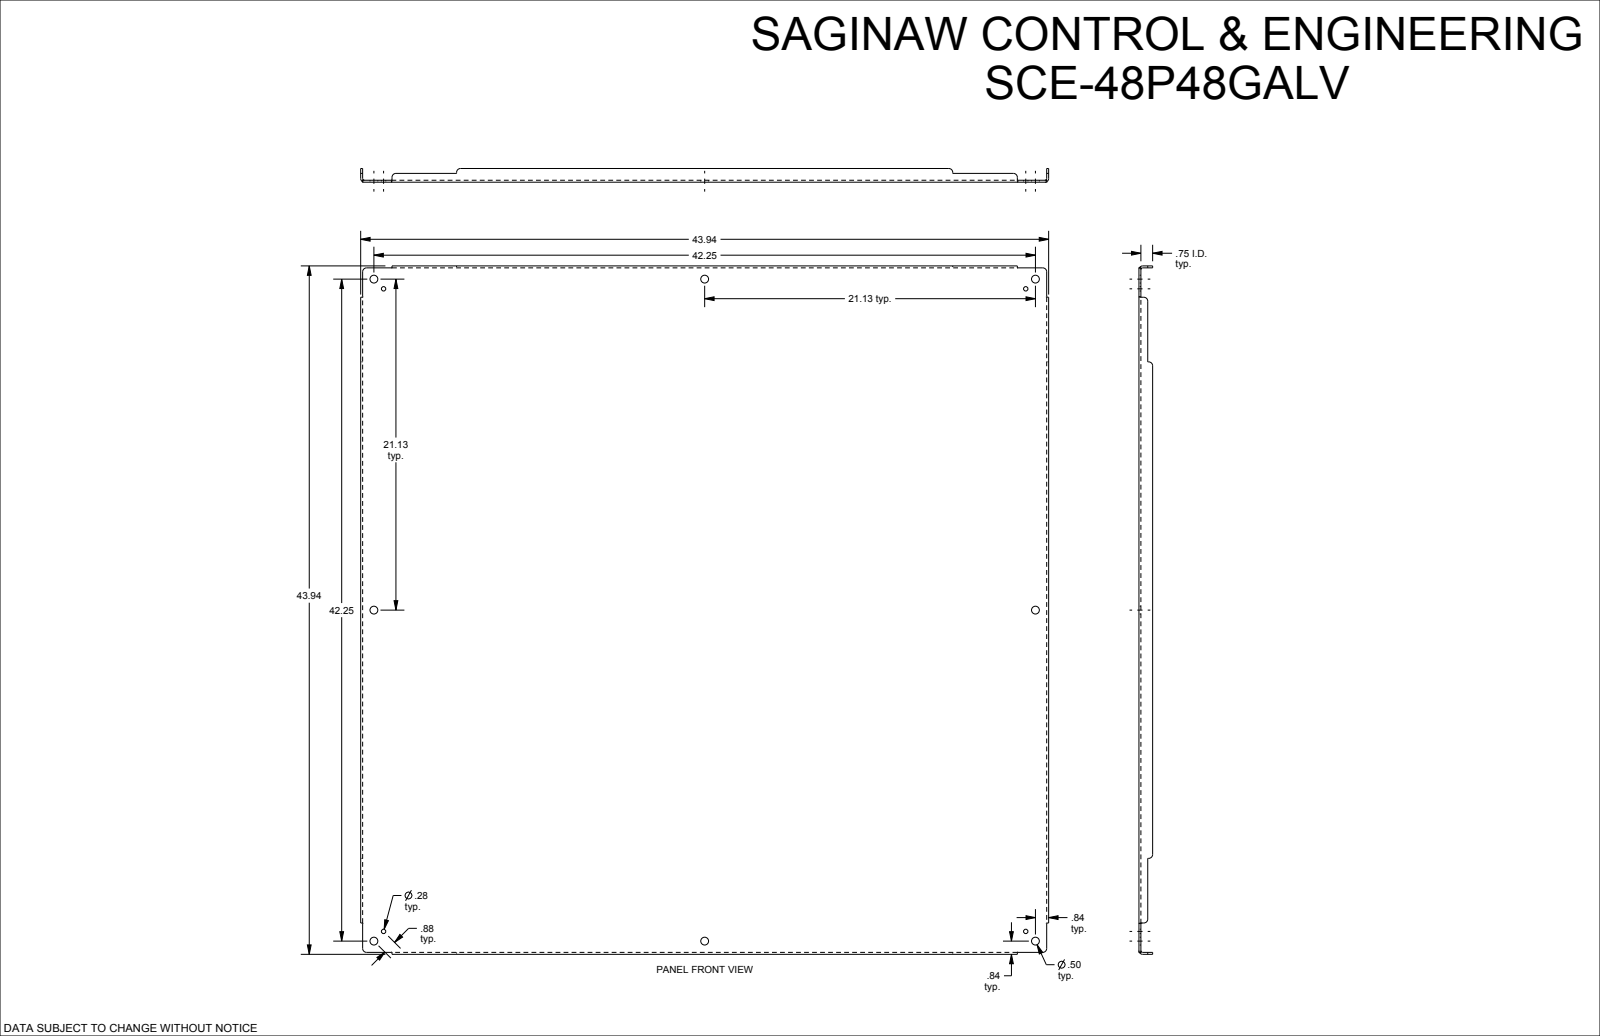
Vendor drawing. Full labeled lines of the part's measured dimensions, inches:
Part name (STEP PRODUCT): SCE-48P48GALV
STEP written by: SolidWorks 2019 (CONFIG_CONTROL_DESIGN)
Units: inches
Bodies: 1 solid, 110 faces (46 planar, 40 cylindrical, 24 other)
Overall size (bounding box): 43.938 × 43.938 × 0.875
Volume: 253 in³ · Surface area: 4 072 in²
Round holes (diameter × count): ⌀0.5 ×8, ⌀0.281 ×4
Partial cylindrical surfaces — rounded edges, fillets, slot ends (radius × count): R0.25 ×12, R0.112 ×4, R0.237 ×4
Main face-to-face distances: 0.125, 0.125, 43.813, 43.687, 43.938, 0.75, 0.875, 0.312, 0.438, 0.563
Hole centre spacings: 20.516, 21.125, 41.636, 46.407, 47.237, 42.25, 0.875, 29.875
